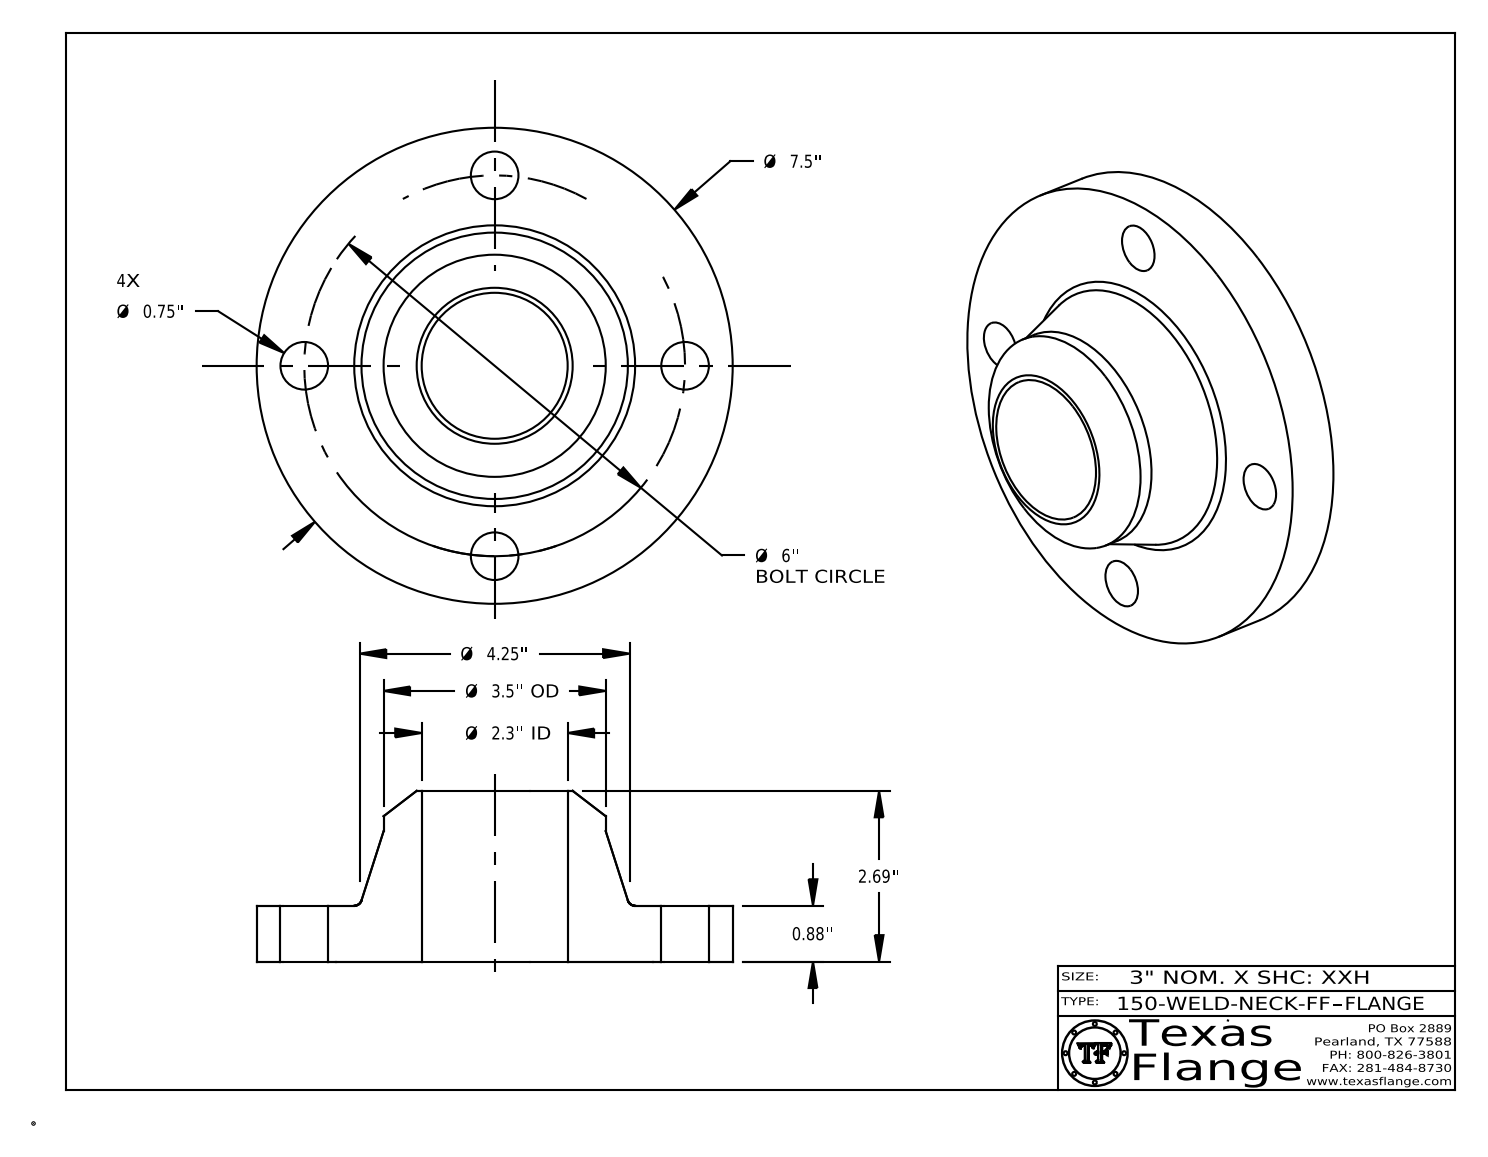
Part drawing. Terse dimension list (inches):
name: 150-WELD-NECK-FF
written by: CATIA V5 STEP AP214 (AUTOMOTIVE_DESIGN)
unit: in
bodies: 1 solid, 409 faces (369 planar, 34 cylindrical, 6 other)
size: 7.5 × 7.5 × 2.69
volume: 45.14 in³; area: 139.1 in²
holes: 4× ⌀0.75, 1× ⌀0.495, 1× ⌀2.3
bosses: 8× ⌀0.03, 1× ⌀7.5, 1× ⌀3.5, 1× ⌀0.39
face distances: 0.88, 2.69, 1.81, 0.865, 0.015, 1.825, 0.148, 0.144, 0.027, 0.096
hole spacings: 3, 4.243, 2.296, 5.543, 6
